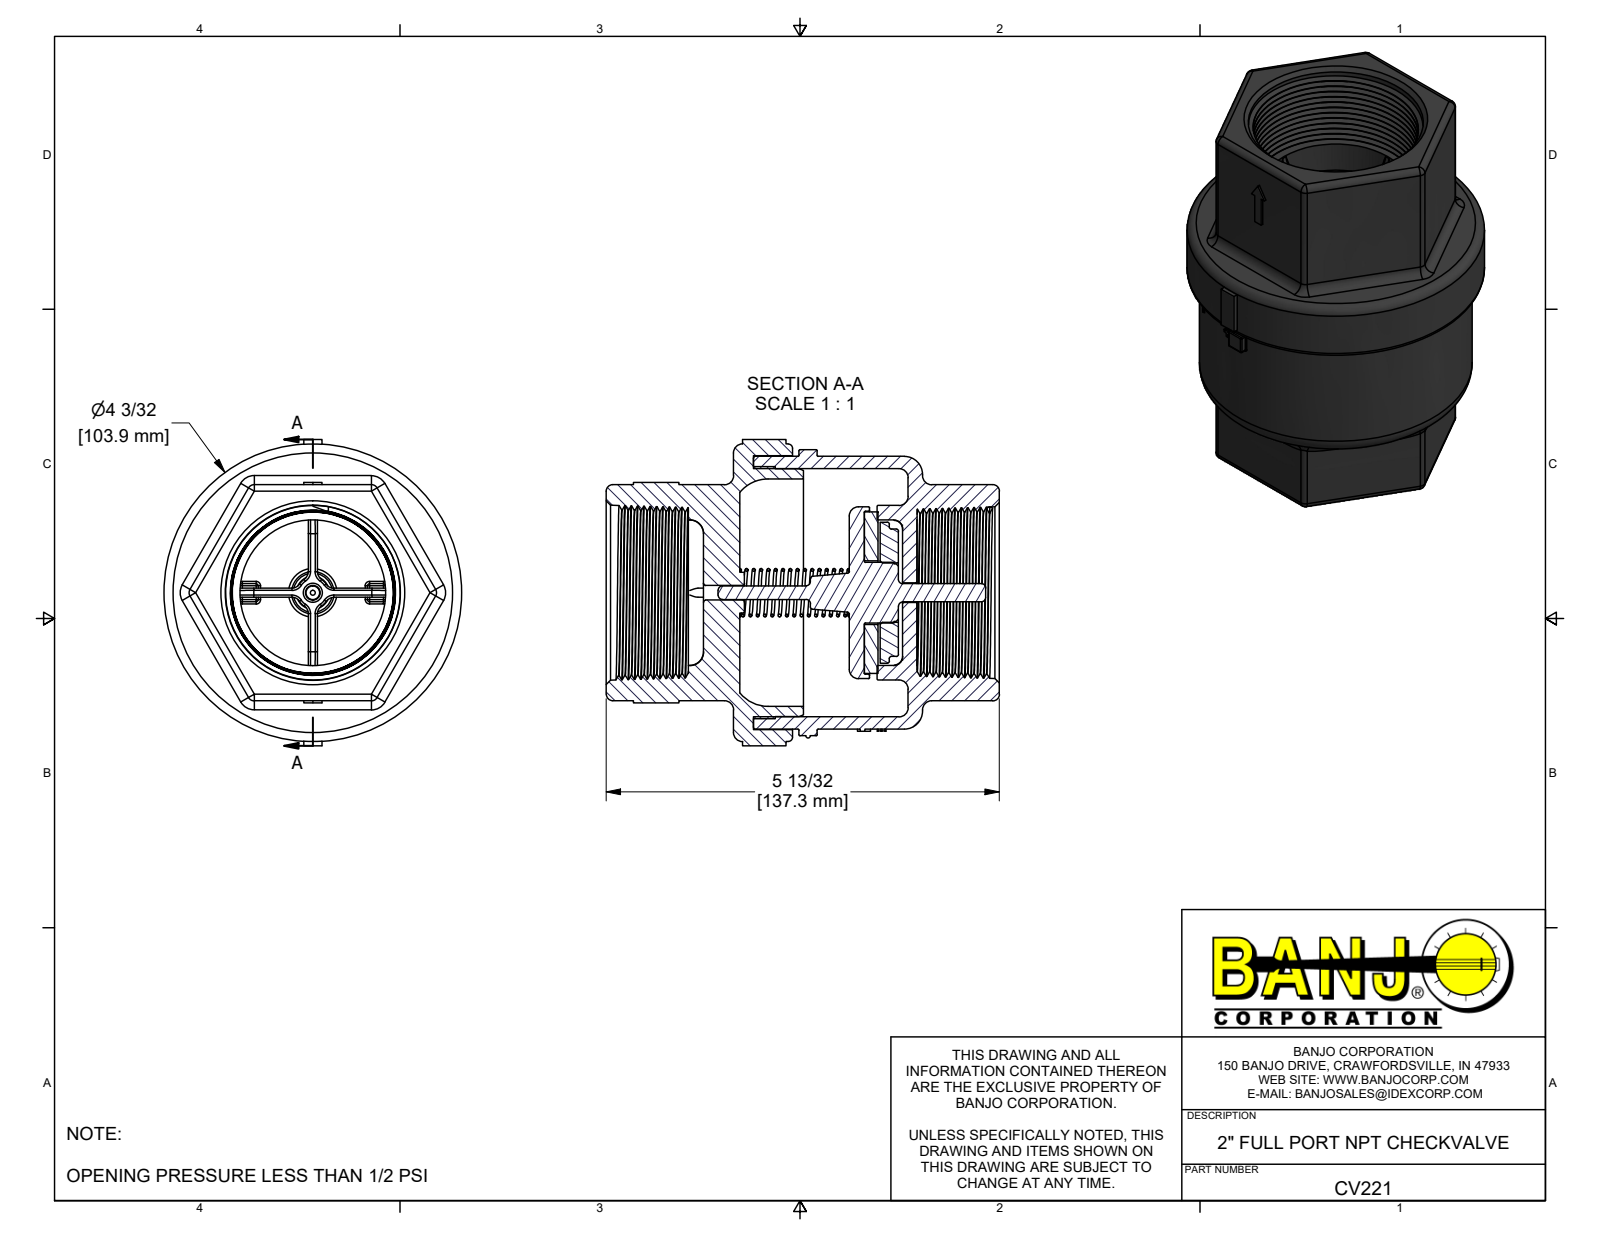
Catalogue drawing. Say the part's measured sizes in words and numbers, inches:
The part is named "CV221; CV25354; CV25354X; CV25356 (+5 more)". Its 3-D file was written by "Autodesk Inventor 2022 (AUTOMOTIVE_DESIGN)". It is 6 solids with 768 faces: 265 planar, 203 cylindrical and 300 other. Overall it measures 5.405 by 4.21 by 4.09 inches. Its volume is 23.4 cubic inches and its surface area 219.2 square inches. Round holes: 1 of diameter 0.2, 1 of diameter 0.27, 1 of diameter 0.814, 1 of diameter 0.875, 1 of diameter 2, 1 of diameter 2.24, 1 of diameter 3.125, 1 of diameter 3.41, 1 of diameter 3.765. Round bosses or shafts: 1 of diameter 4.09, 1 of diameter 3.75, 1 of diameter 3.465, 1 of diameter 3.405, 1 of diameter 2.4, 1 of diameter 2.36, 1 of diameter 2.219, 1 of diameter 1.937. Partial cylindrical surfaces (rounded edges, fillets, slot ends): 40 of radius 0.03, 24 of radius 0.06, 23 of radius 0.015, 20 of radius 0.125, 18 of radius 0.09, 1 of radius 0.219, 1 of radius 0.22, 1 of radius 0.28. The main face-to-face distances are 2.97, 1.713, 0.207, 0.188, 1.525, 0.395, 1.317, 1.988, 1.8, 1.593.
